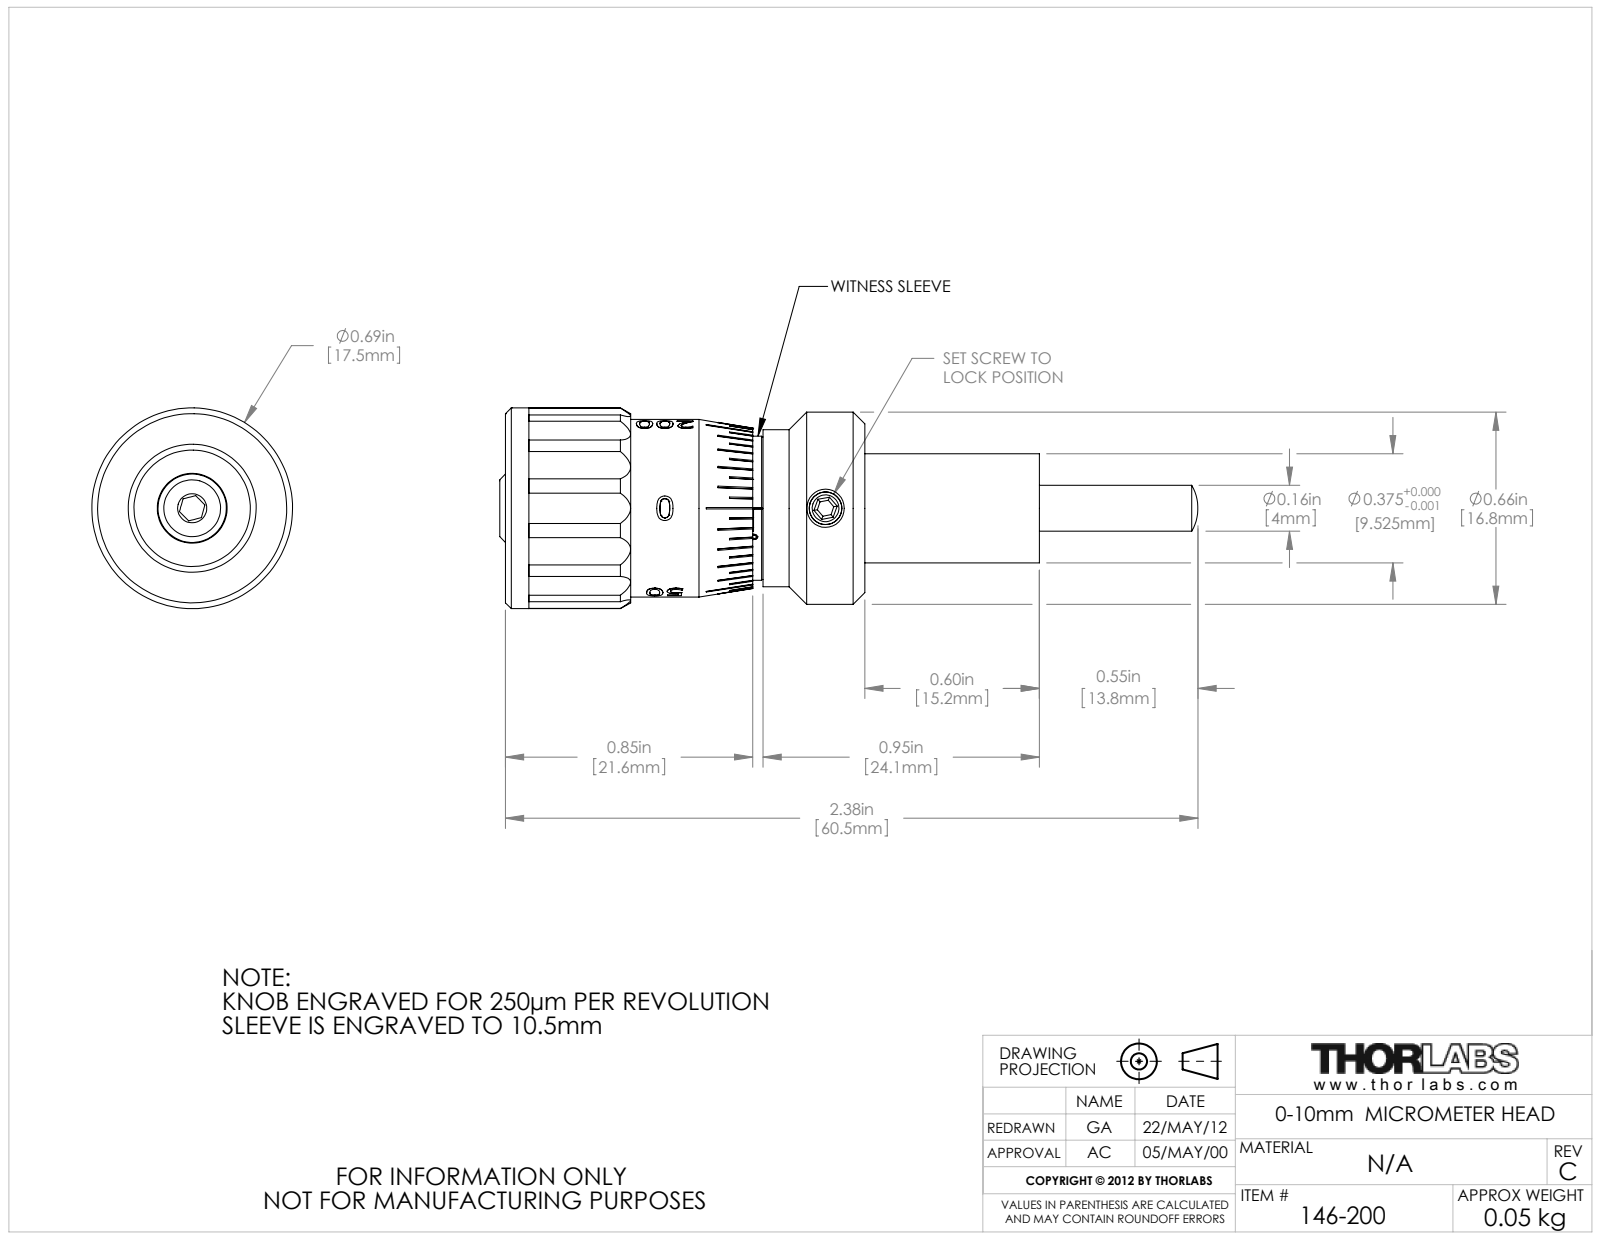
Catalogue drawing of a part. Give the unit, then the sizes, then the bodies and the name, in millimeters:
Units: millimetres
Overall size (bounding box): 61 × 17.5 × 17.5
Round holes (diameter × count): ⌀2.6 ×1, ⌀2.8 ×1, ⌀3.2 ×1, ⌀3.6 ×1, ⌀4 ×1, ⌀4 ×1, ⌀4 ×1, ⌀4.7 ×1, ⌀6.1 ×1, ⌀10.2 ×1, ⌀10.5 ×1, ⌀11 ×1
Round bosses / shafts (diameter × count): ⌀17.5 ×1, ⌀16.8 ×1, ⌀15.5 ×1, ⌀13.7 ×1, ⌀12.6 ×1, ⌀12.4 ×1, ⌀11.2 ×1, ⌀10.5 ×1
Partial cylindrical surfaces — rounded edges, fillets, slot ends (radius × count): R2.4 ×14, R6.3 ×1, R7.8 ×1
Main face-to-face distances: 0.8, 27.8, 2, 29.8, 15.5, 22.1, 21.6, 1.5, 20.6, 7.2
Volume: 7 050 mm³ · Surface area: 7 716 mm²
Bodies: 10 solids, 973 faces (479 planar, 140 cylindrical, 354 other)
Part name (STEP PRODUCT): 3129-E0W
STEP written by: SolidWorks 2012 (AUTOMOTIVE_DESIGN)
